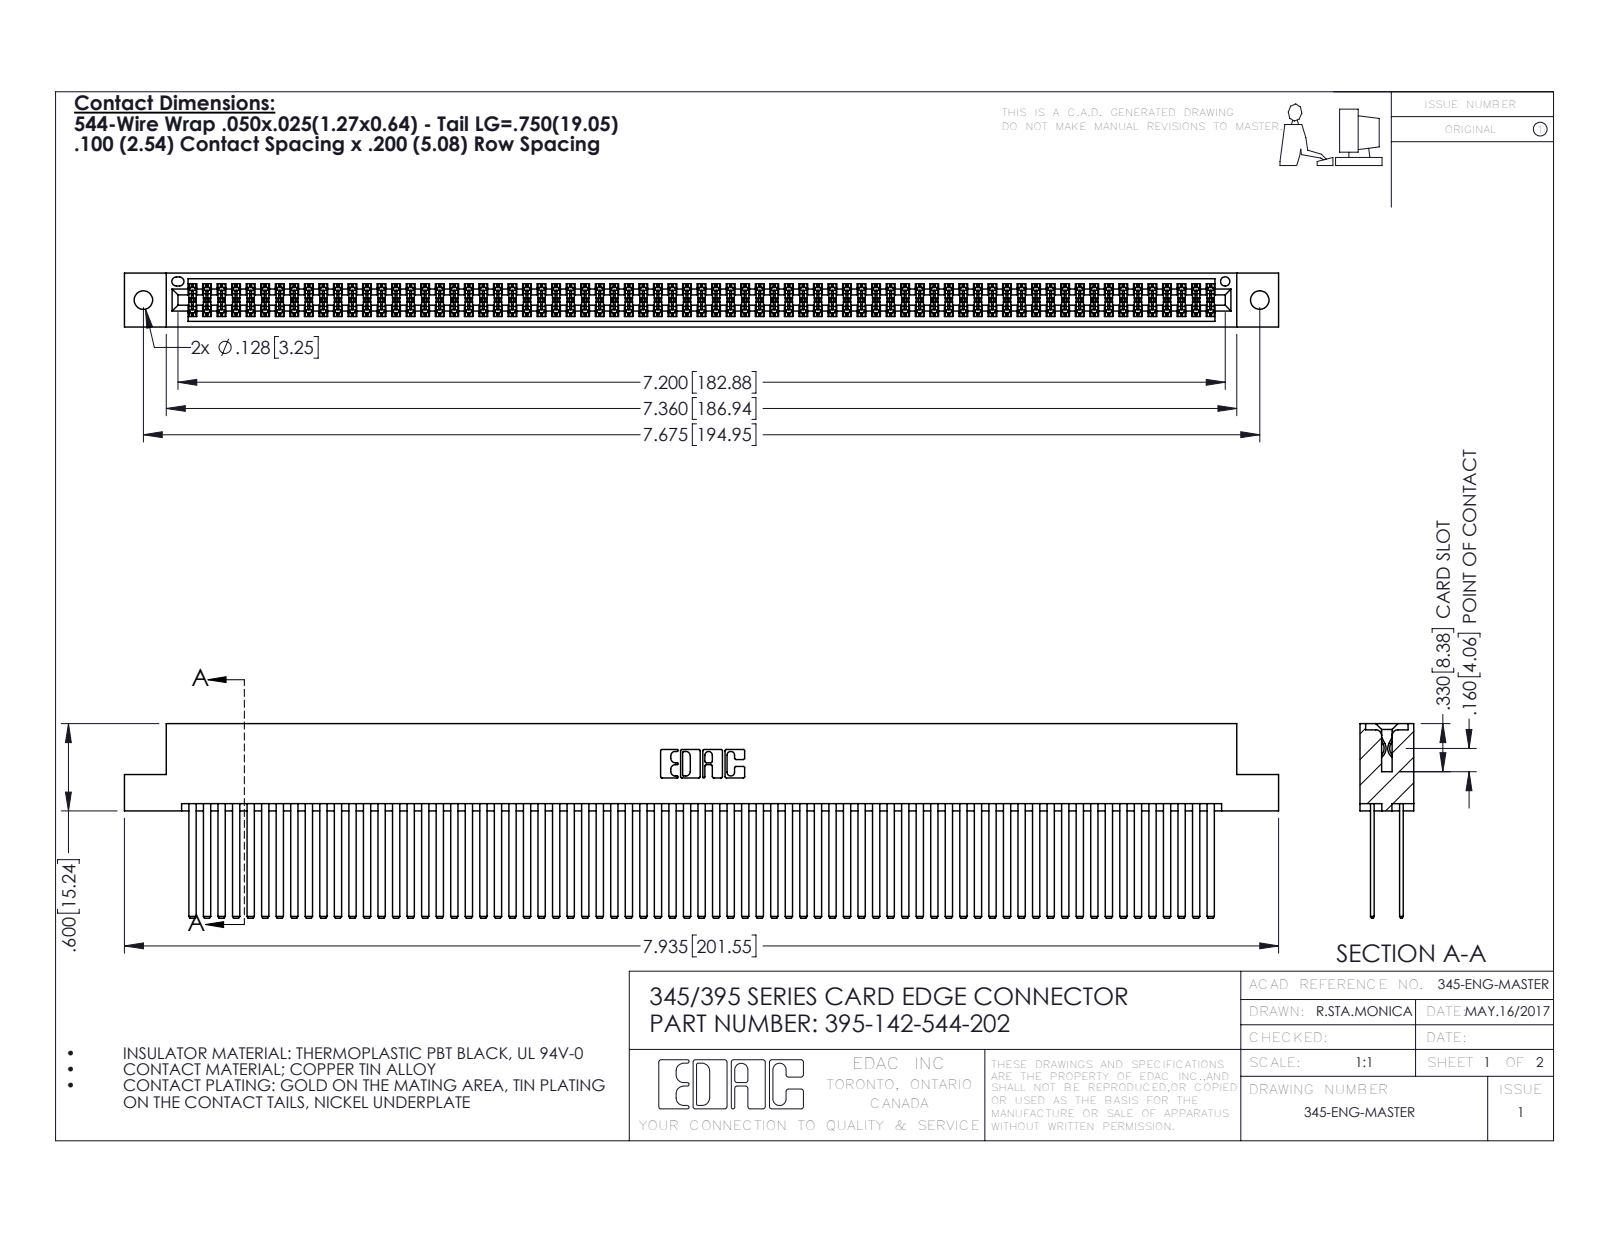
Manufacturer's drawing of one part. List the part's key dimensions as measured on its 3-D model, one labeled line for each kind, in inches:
Part name (STEP PRODUCT): 395-142-544-202; 345 Part_Flush Mounting Lugs - 0.128 Dia; 345-292-001_345-293-144
STEP written by: SolidWorks 2016 (CONFIG_CONTROL_DESIGN)
Units: inches
Bodies: 143 solids, 6374 faces (4198 planar, 2176 cylindrical, 0 other)
Overall size (bounding box): 7.935 × 1.337 × 0.37
Volume: 1.33 in³ · Surface area: 59.44 in²
Round holes (diameter × count): ⌀0.128 ×2, ⌀0.064 ×1
Partial cylindrical surfaces — rounded edges, fillets, slot ends (radius × count): R0.006 ×213, R0.01 ×22, R0.007 ×6, R0.031 ×6, R0.026 ×3, R0.014 ×2, R0.019 ×2, R0.022 ×2
Main face-to-face distances: 0.2, 0.025, 0.298, 0.072, 0.098, 0.272, 0.225, 0.175, 0.37, 0.05
Hole centre spacings: 0.27, 7.439, 7.675
